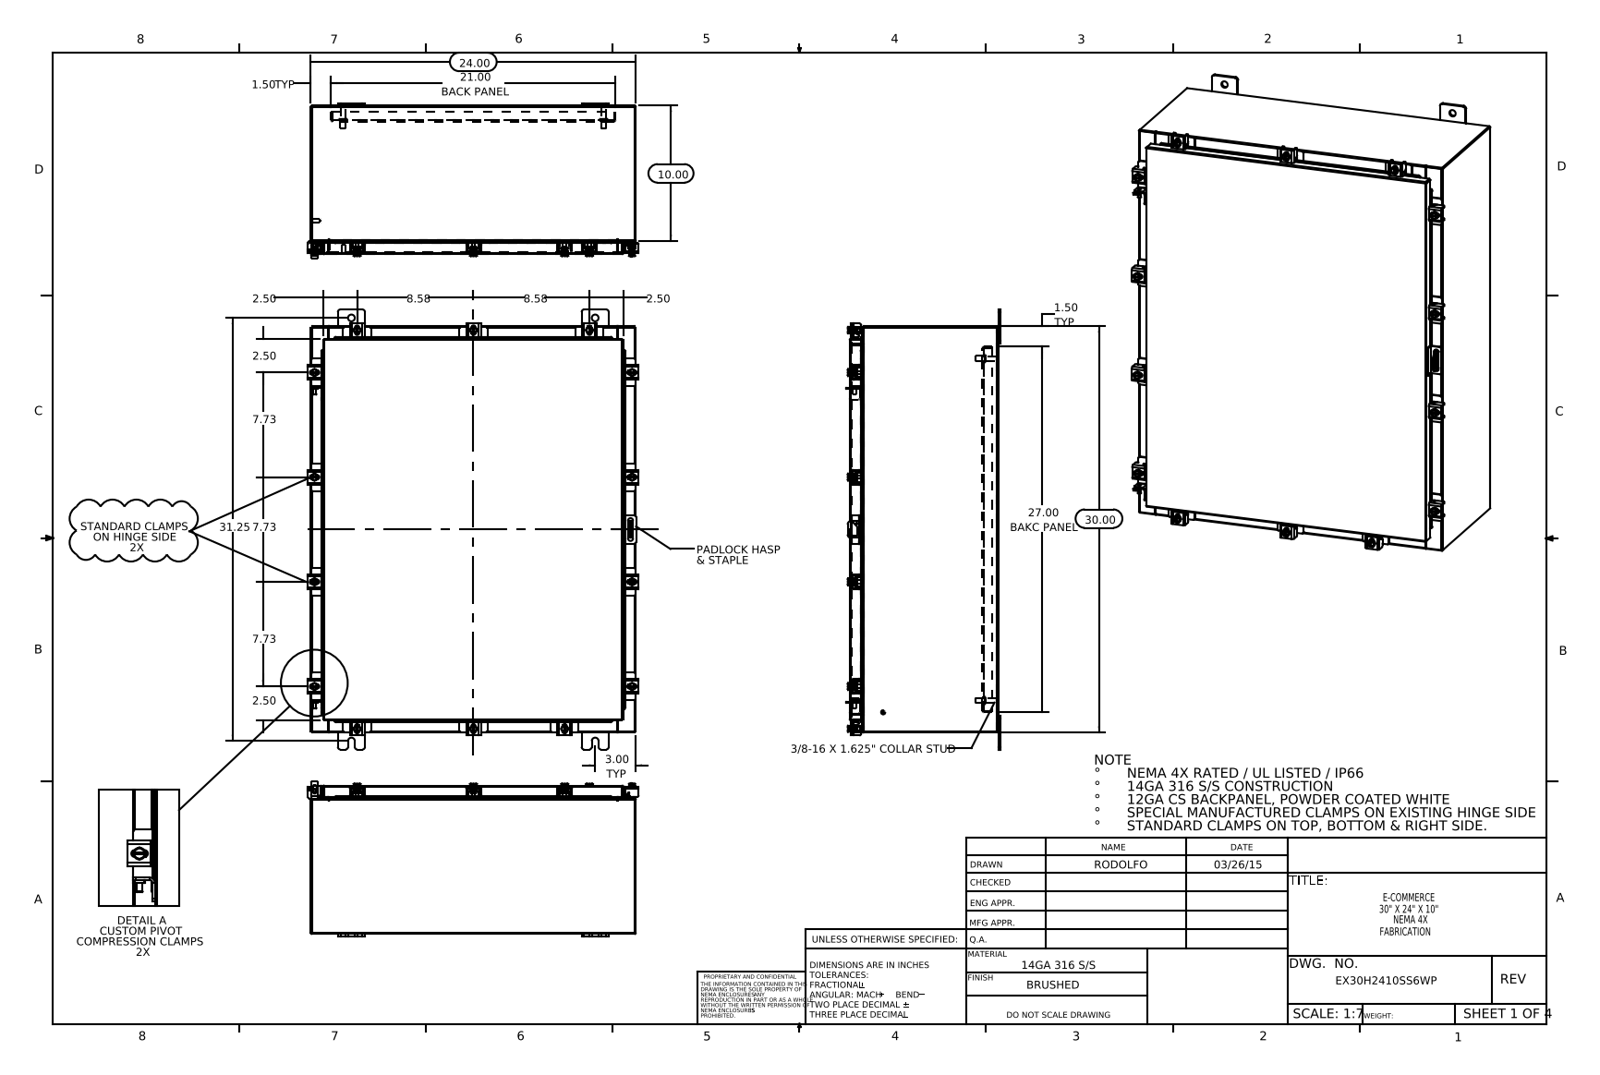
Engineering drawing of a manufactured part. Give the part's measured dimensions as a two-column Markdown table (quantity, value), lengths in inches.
| quantity | value |
| --- | --- |
| part name | EX30H2410SS6WP Bottom; EX30H2410SS6WP Body; 22101002_RTP29; EX30H2410SS6WP Standard Clamps (+8 more) |
| STEP written by | SolidWorks 2014 (CONFIG_CONTROL_DESIGN) |
| units | inches |
| bodies | 91 solids, 2272 faces (1211 planar, 885 cylindrical, 176 other) |
| overall size | 32.5 × 24.421 × 11.453 |
| volume | 280.7 in³ |
| surface area | 7 003 in² |
| round holes (diameter × count) | 0.213 × 14, 0.26 × 14, 0.5 × 8, 0.125 × 1, 0.25 × 1 |
| round bosses / shafts (diameter × count) | 0.5 × 14, 0.25 × 14, 0.399 × 12, 0.625 × 4, 0.375 × 4, 0.33 × 4, 0.315 × 2, 0.236 × 2 |
| partial cylindrical surfaces (radius × count) | 0.06 × 62, 0.141 × 28, 0.013 × 26, 0.12 × 26, 0.19 × 24, 0.088 × 22, 0.09 × 22, 0.05 × 21 |
| main face-to-face distances | 0.075, 10.9, 10.975, 10.826, 0.104, 23.925, 1, 1.075, 9.826, 9.9 |
| hole center spacings | 23.451, 24.31, 32.286, 2.347, 4.44, 20.544, 26.507, 27.37 |
